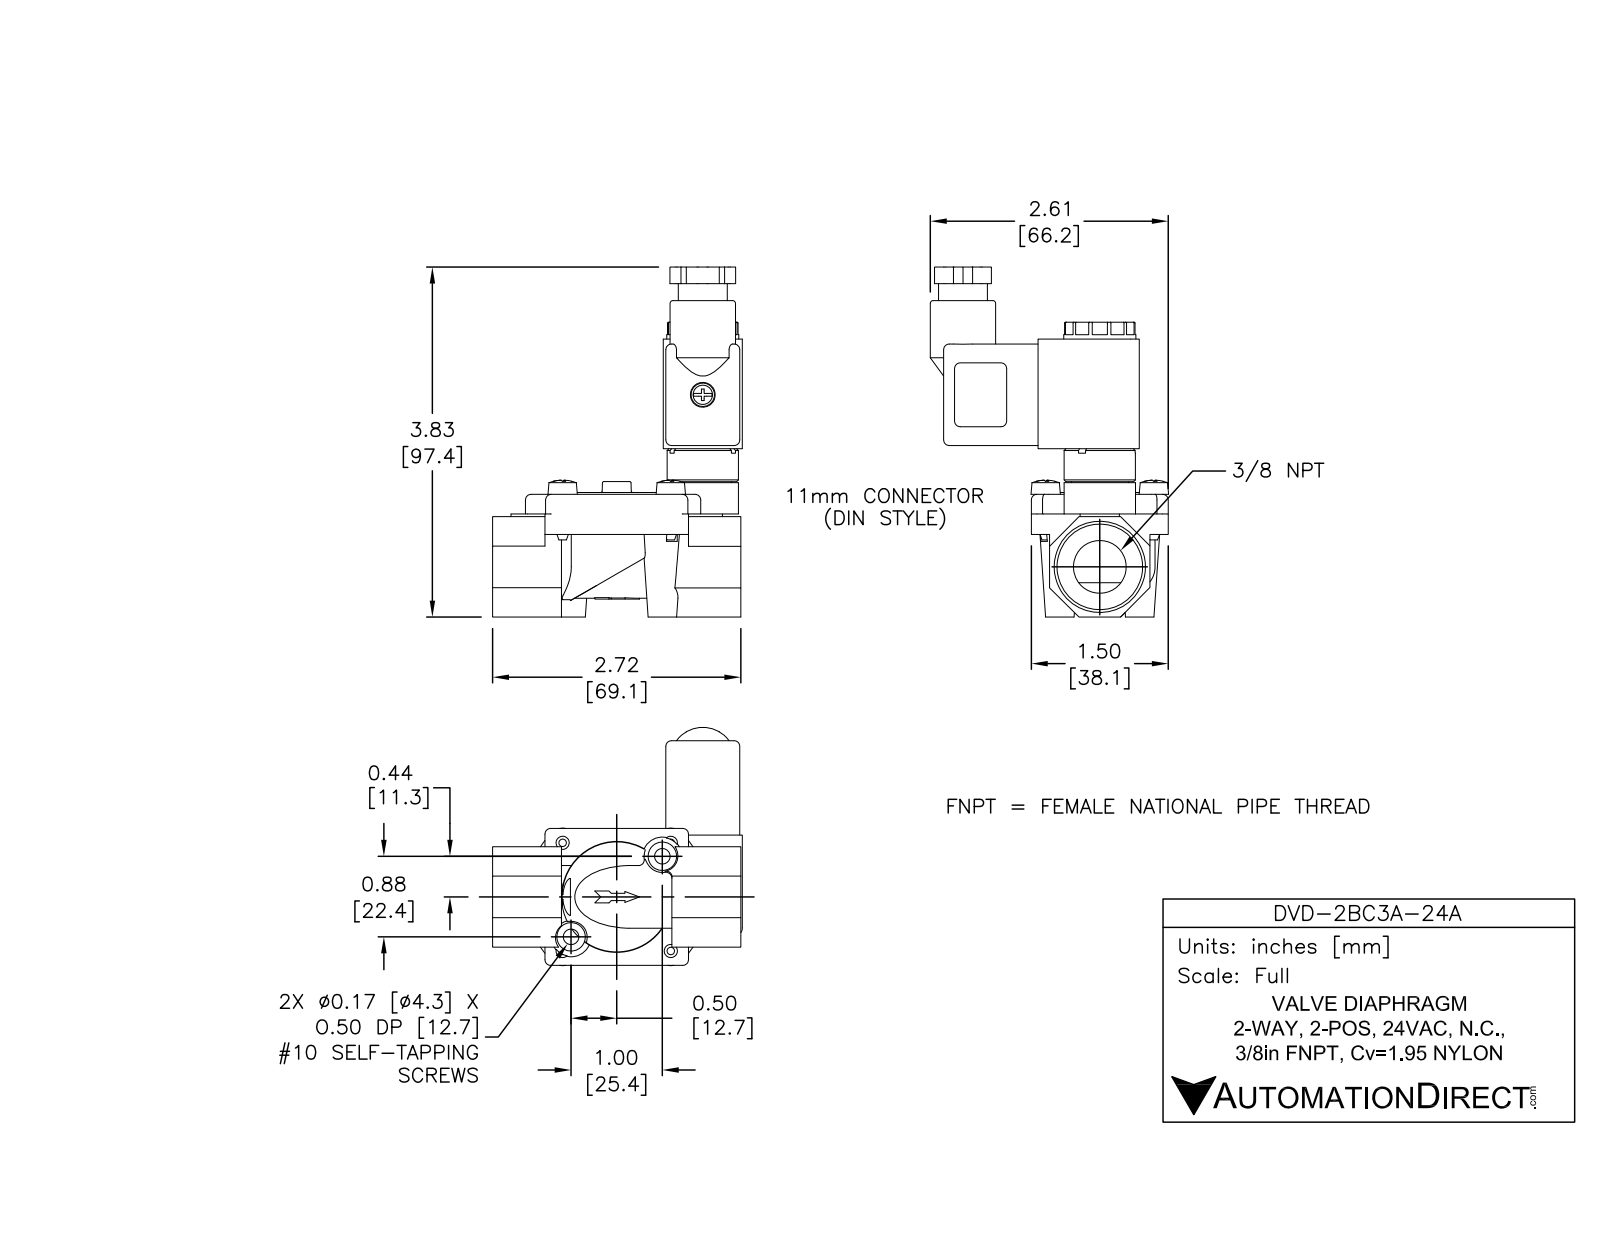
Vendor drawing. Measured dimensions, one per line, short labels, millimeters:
name: DVD-2BC3A-24A
written by: SolidWorks 2015 (AUTOMOTIVE_DESIGN)
unit: mm
bodies: 13 solids, 1441 faces (721 planar, 253 cylindrical, 467 other)
size: 97.4 × 69.5 × 66.3
volume: 65 810 mm³; area: 40 110 mm²
holes: 4× ⌀3.7, 4× ⌀4.2, 2× ⌀1.5, 2× ⌀2.4, 2× ⌀4.3, 2× ⌀14.7, 1× ⌀1.6, 1× ⌀4, 1× ⌀4.2, 1× ⌀6.4, 1× ⌀6.9, 1× ⌀7.9
bosses: 4× ⌀4.7, 4× ⌀3.2, 2× ⌀15.9, 1× ⌀34.9, 1× ⌀20.1, 1× ⌀19.9, 1× ⌀19.8, 1× ⌀18.2
rounds: 24× R0.3, 24× R1.6, 12× R4, 3× R1.1, 2× R2.4, 2× R5.5, 1× R7.7, 1× R8.7
face distances: 1.3, 27.9, 22, 19.3, 5.1, 33, 20, 2, 2, 18
hole spacings: 21.3, 30.1, 4.6, 16.9, 17.5, 26.3, 28, 38.2
